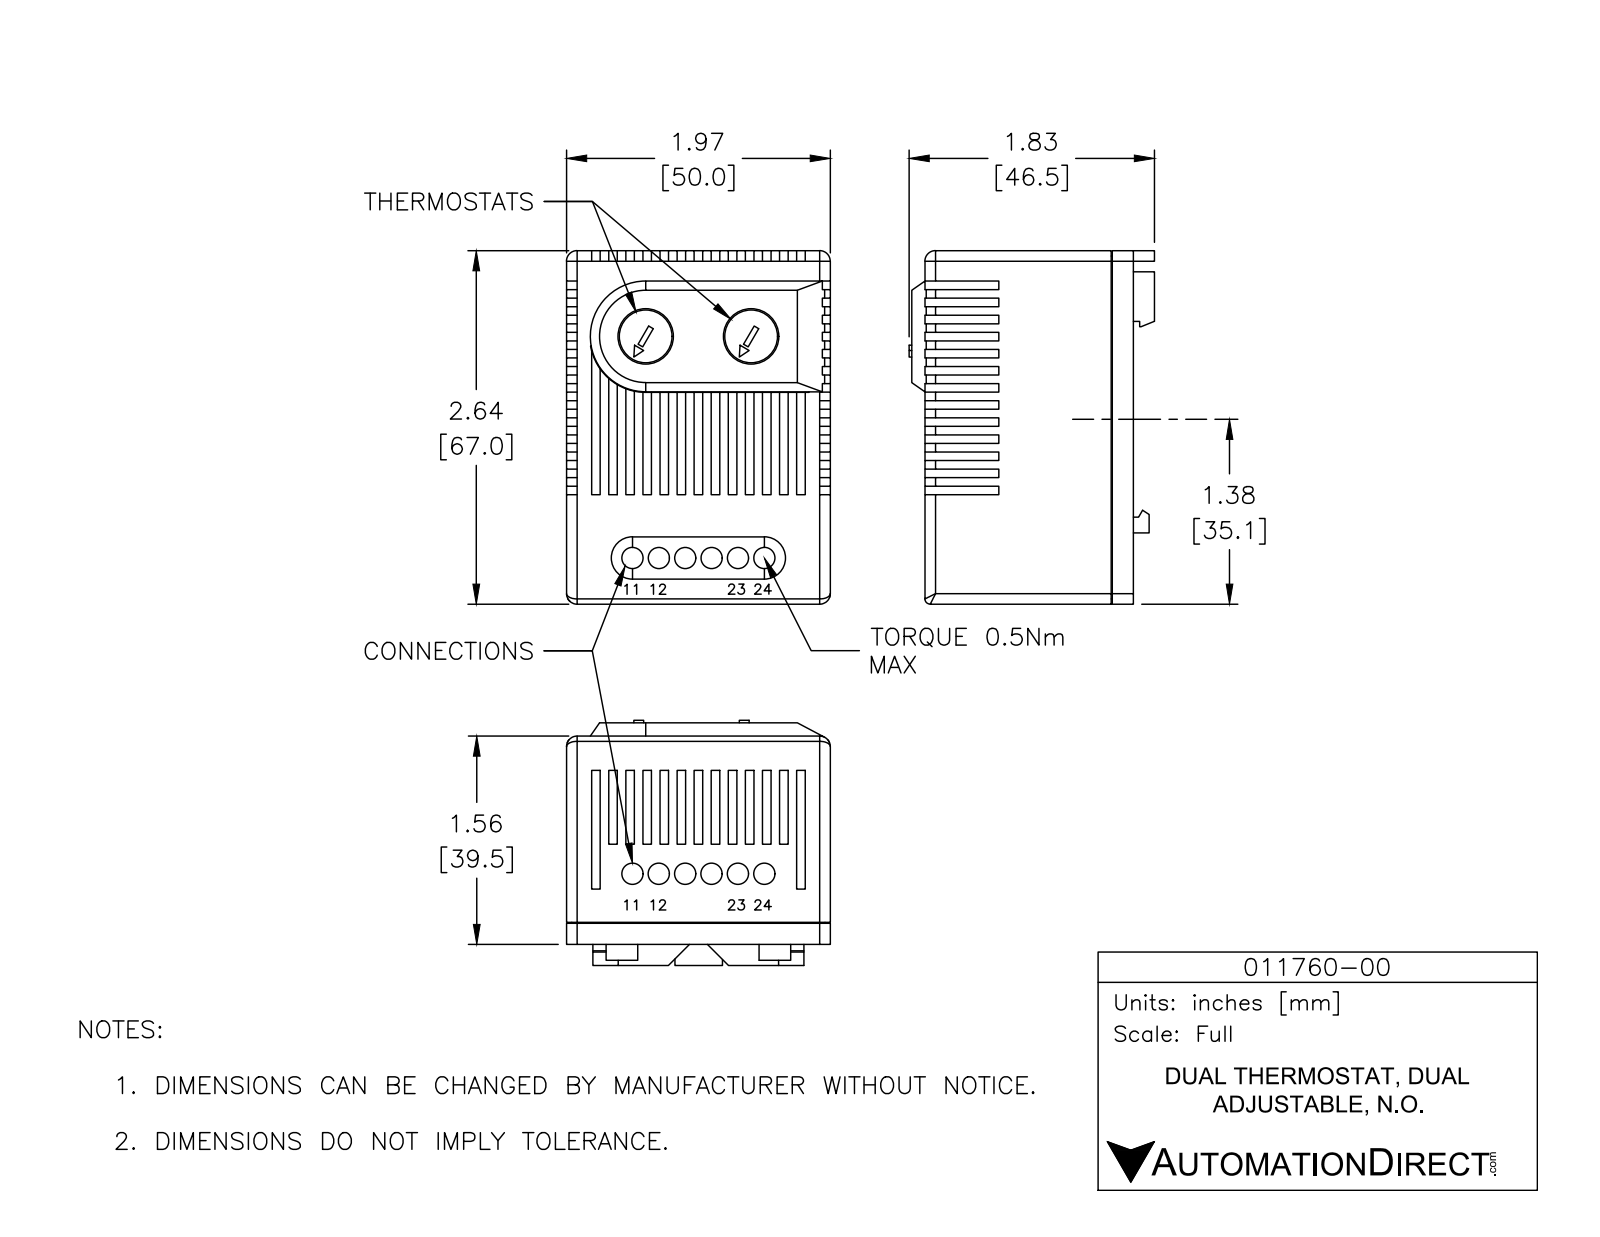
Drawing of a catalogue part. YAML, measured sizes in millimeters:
part_name: "011760-00"
step_written_by: "SolidWorks 2017 (AUTOMOTIVE_DESIGN)"
units: millimeters
bodies: {solids: 2, faces: 656, planar: 507, cylindrical: 93, other: 56}
overall_size: [67.5, 50, 46.5]
volume: 130100
surface_area: 23190
round_holes:
  - {diameter: 4, count: 12}
  - {diameter: 10.5, count: 2}
round_bosses_or_shafts:
  - {diameter: 10, count: 2}
partial_cylinders:
  - {radius: 2, count: 7}
  - {radius: 1, count: 5}
  - {radius: 1.4, count: 1}
  - {radius: 1.5, count: 1}
  - {radius: 4, count: 1}
  - {radius: 10.5, count: 1}
  - {radius: 10.6, count: 1}
face_to_face_distances: [50, 2, 3.3, 39.5, 67, 1.6, 6.5, 9.7, 4.9, 8.1]
hole_center_spacings: [5, 10, 15, 20, 42.1, 25, 42.7, 43.8]
